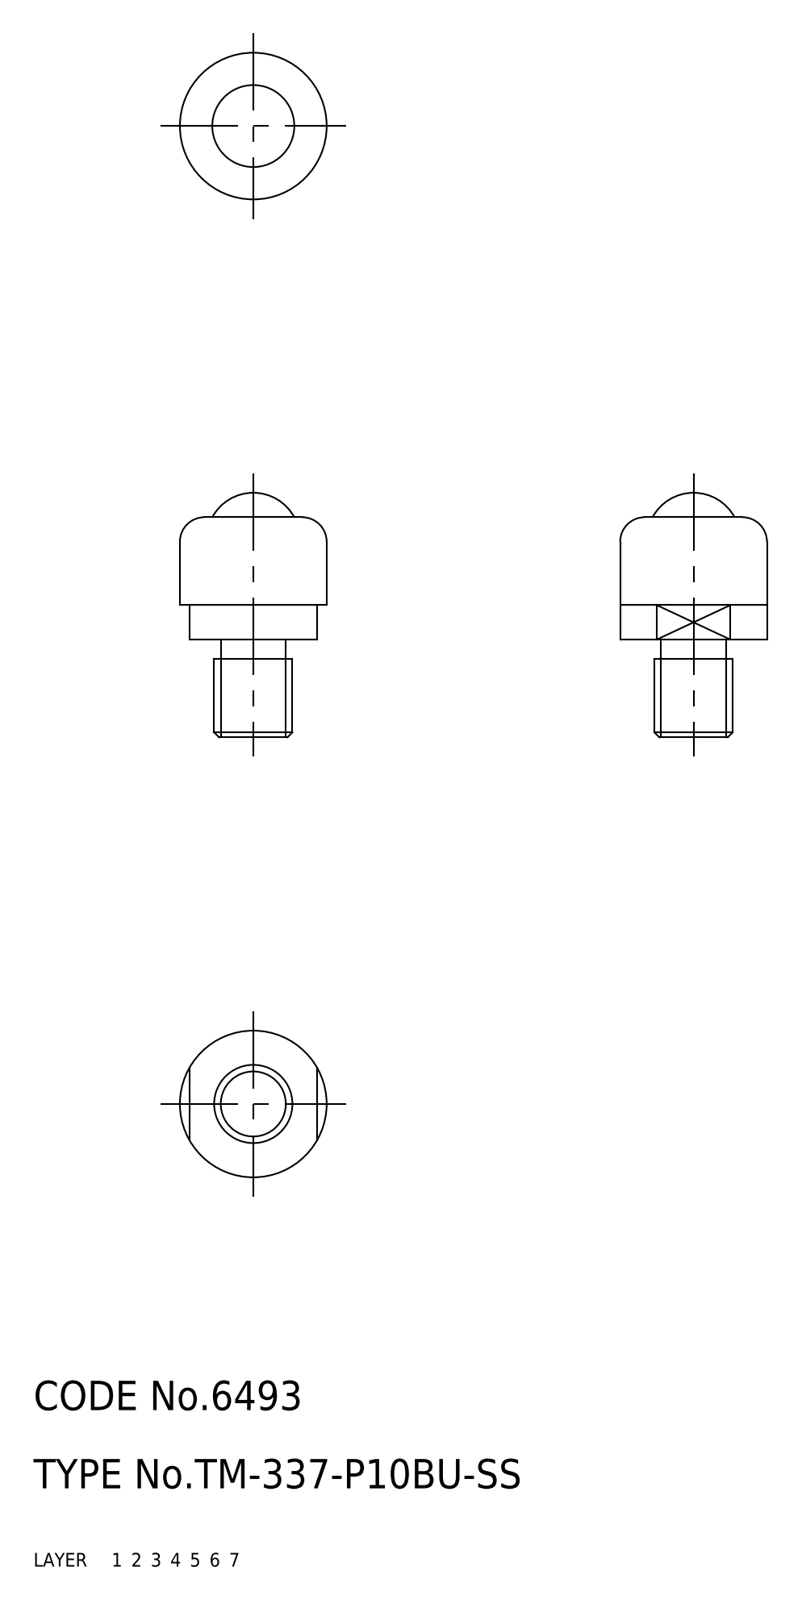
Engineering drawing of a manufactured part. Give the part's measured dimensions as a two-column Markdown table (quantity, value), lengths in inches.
| quantity | value |
| --- | --- |
| part name | housing; pan; TM_337_P10BU_SS; ball_A |
| STEP written by | SolidWorks 2015 (AUTOMOTIVE_DESIGN) |
| units | inches |
| bodies | 3 solids, 29 faces (9 planar, 12 cylindrical, 8 other) |
| overall size | 0.984 × 0.591 × 0.591 |
| volume | 0.111 in³ |
| surface area | 3.075 in² |
| round holes (diameter × count) | 0.354 × 1, 0.535 × 1 |
| round bosses / shafts (diameter × count) | 0.591 × 1, 0.315 × 1, 0.262 × 1 |
| main face-to-face distances | 0.138, 0.394, 0.531, 0.512, 0.315, 0.079, 0.217, 0.858, 0.543, 0.465 |
